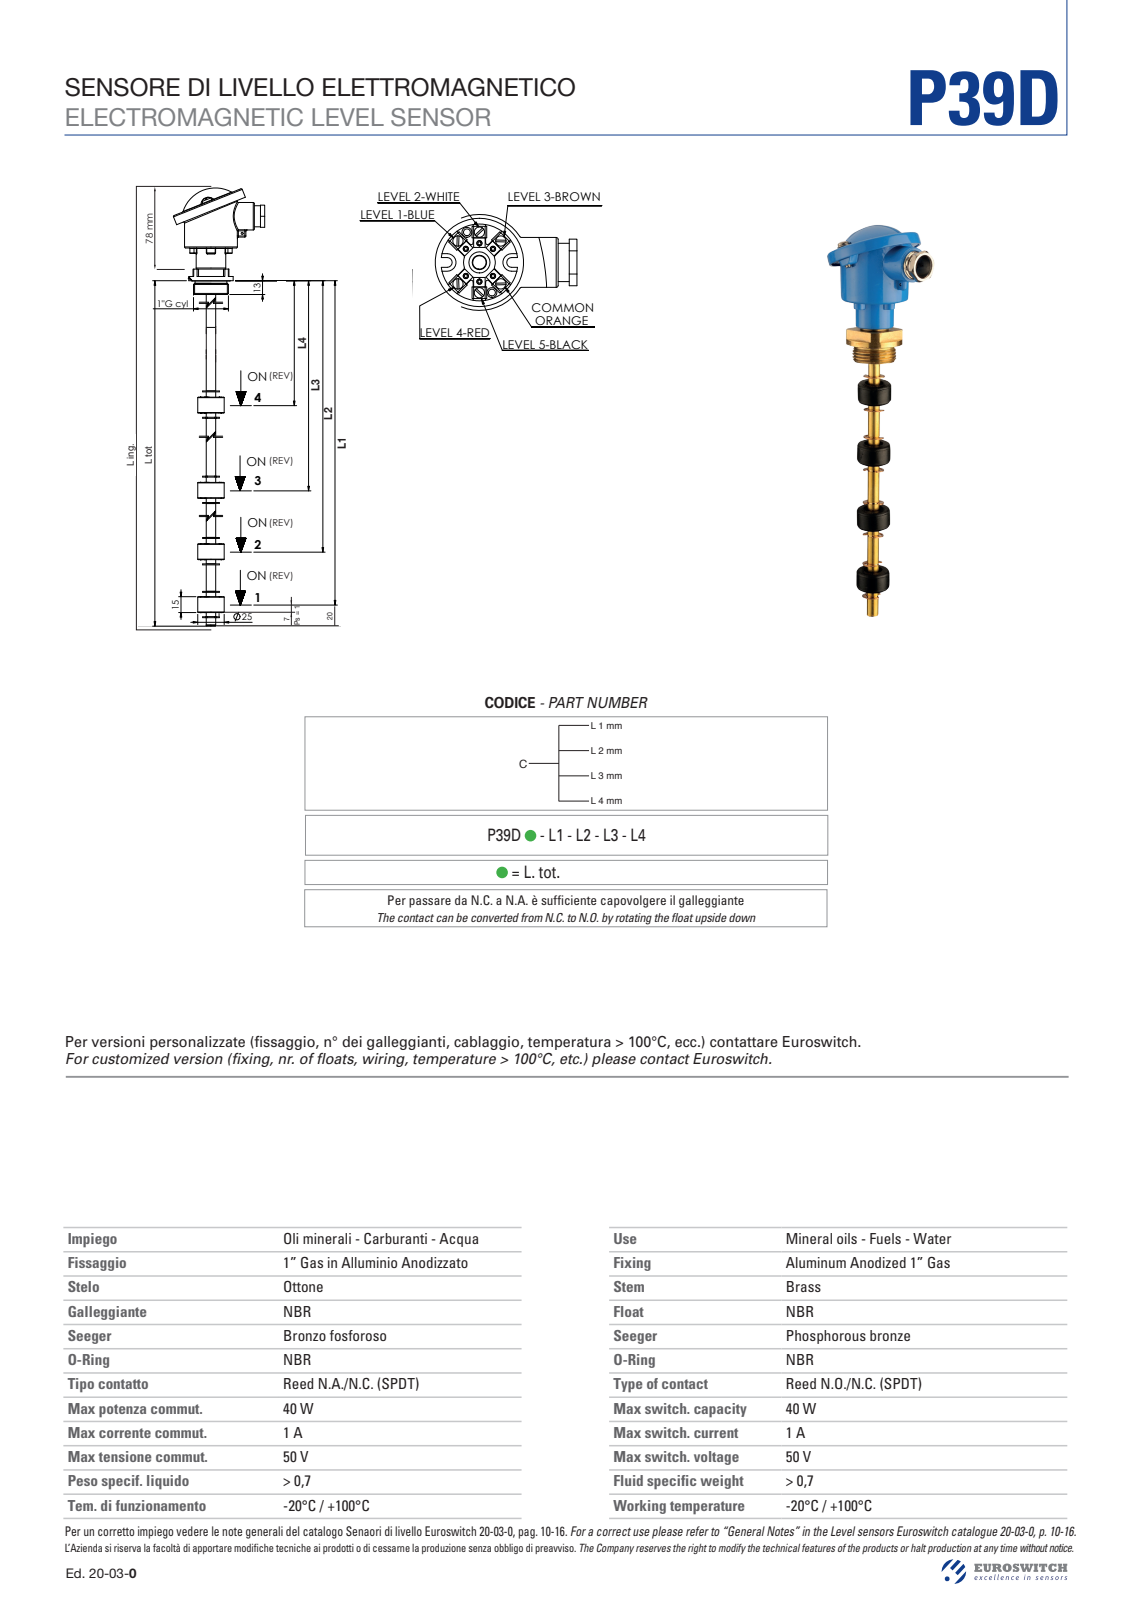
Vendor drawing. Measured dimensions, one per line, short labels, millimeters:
name: P39D
written by: SolidWorks 2019 (AUTOMOTIVE_DESIGN)
unit: mm
bodies: 0 solids, 546 faces (244 planar, 184 cylindrical, 118 other)
size: 222.79 × 86.34 × 70
holes: 1× ⌀2, 1× ⌀10.3, 1× ⌀10.65, 1× ⌀13, 1× ⌀15.76, 1× ⌀16, 1× ⌀38.6
bosses: 2× ⌀10, 2× ⌀9.15, 1× ⌀70, 1× ⌀50, 1× ⌀42, 1× ⌀33.2, 1× ⌀33, 1× ⌀30
rounds: 16× R0.5, 9× R1, 7× R0.8, 4× R1.1, 4× R4, 2× R7, 1× R6.05
face distances: 9, 20, 24, 15, 44, 34, 45, 27, 4, 31
